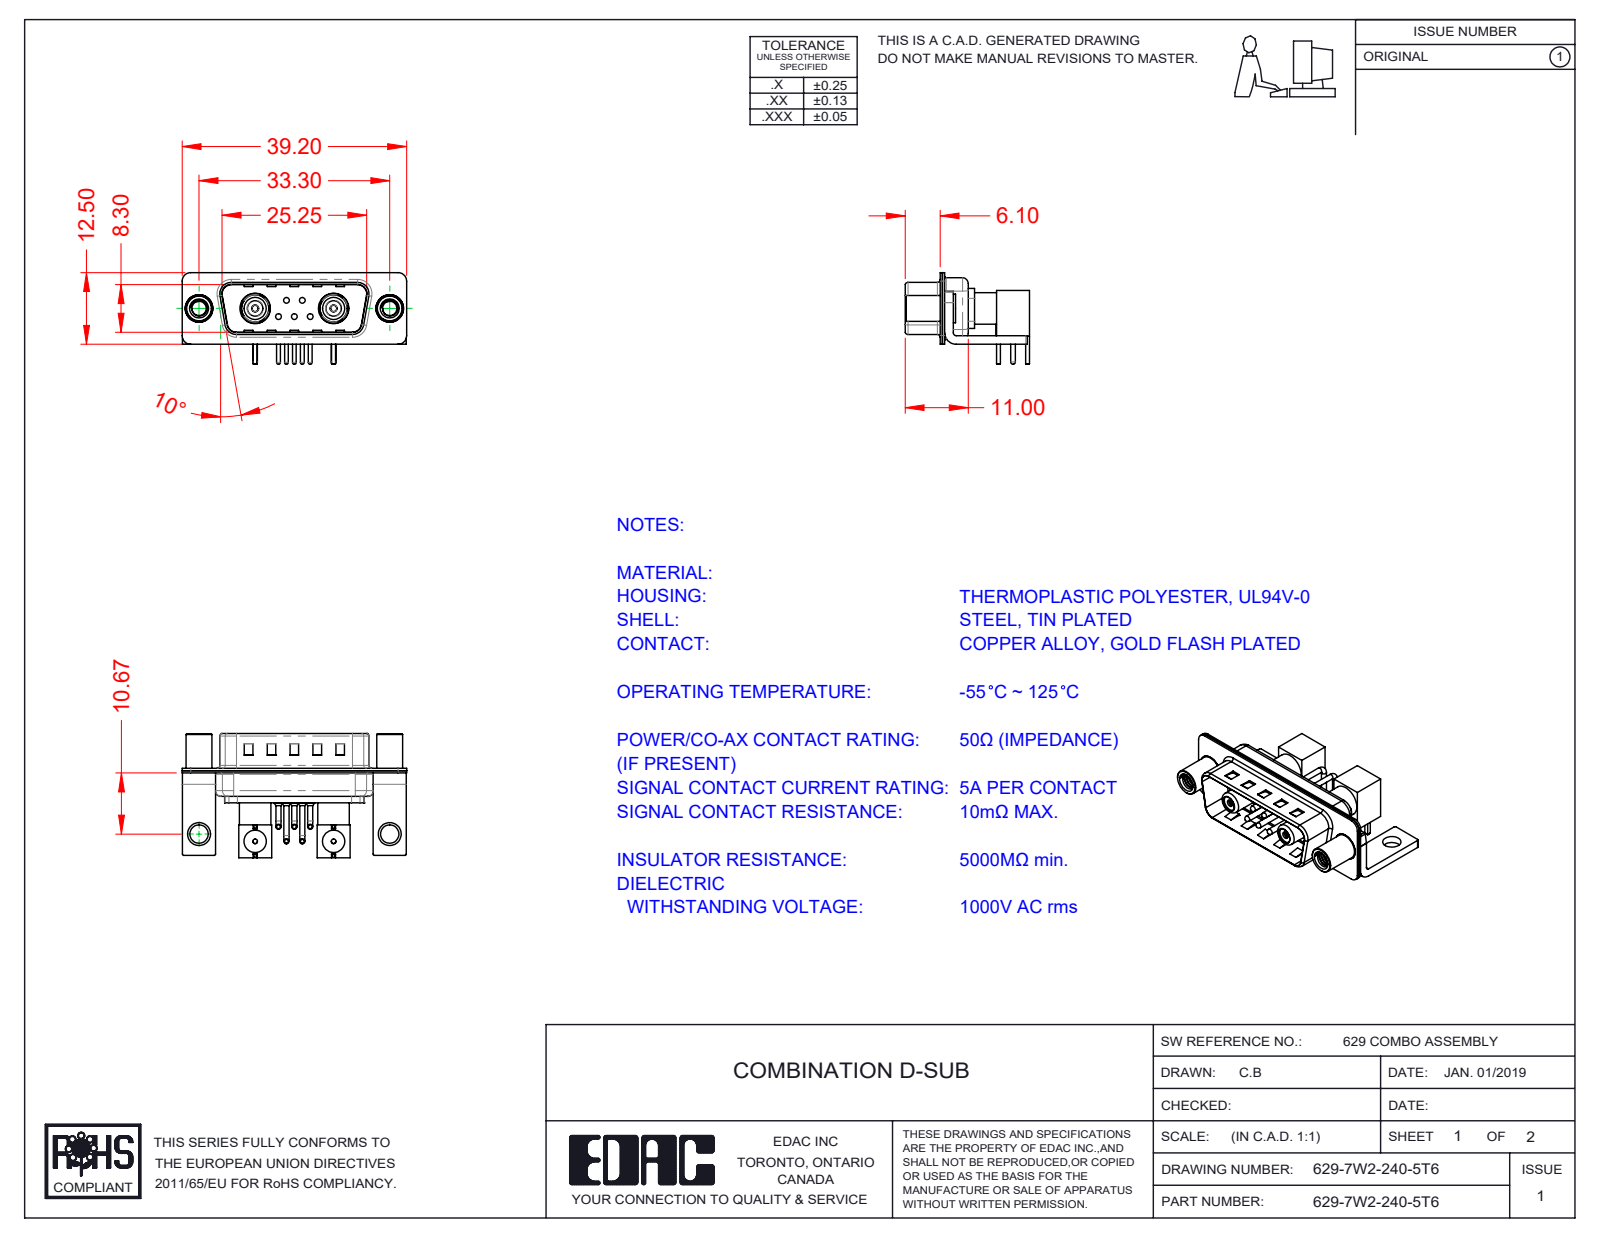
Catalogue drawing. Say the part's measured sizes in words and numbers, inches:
The part is named "Insulator Socket; 629Combo Threaded Standoff_D; Co-Ax Jack Assy_RA; 629Combo Housing_7W2 (+8 more)". Its 3-D file was written by "SolidWorks 2020 (CONFIG_CONTROL_DESIGN)". It is 26 solids with 1292 faces: 595 planar, 519 cylindrical and 178 other. Overall it measures 1.543 by 0.855 by 0.63 inches. Its volume is 0.173 cubic inches and its surface area 11.95 square inches. Round holes: 7 of diameter 0.063, 5 of diameter 0.03, 5 of diameter 0.079, 4 of diameter 0.098, 2 of diameter 0.031, 2 of diameter 0.043, 2 of diameter 0.047, 2 of diameter 0.059, 2 of diameter 0.106, 2 of diameter 0.122, 2 of diameter 0.126, 2 of diameter 0.134. Round bosses or shafts: 10 of diameter 0.035, 5 of diameter 0.059, 5 of diameter 0.039, 5 of diameter 0.026, 4 of diameter 0.031, 2 of diameter 0.217, 2 of diameter 0.205, 2 of diameter 0.197. Partial cylindrical surfaces (rounded edges, fillets, slot ends): 16 of radius 0.01, 16 of radius 0.059, 13 of radius 0.079, 9 of radius 0.02, 8 of radius 0.063, 5 of radius 0.04, 4 of radius 0.024, 4 of radius 0.026. The main face-to-face distances are 0.016, 0.031, 0.059, 0.374, 0.358, 0.343, 0.226, 0.39, 0.014, 0.024. The hole center spacings are 0.539, 0.124, 0.389, 0.926, 0.109, 0.386, 0.925, 1.311.
